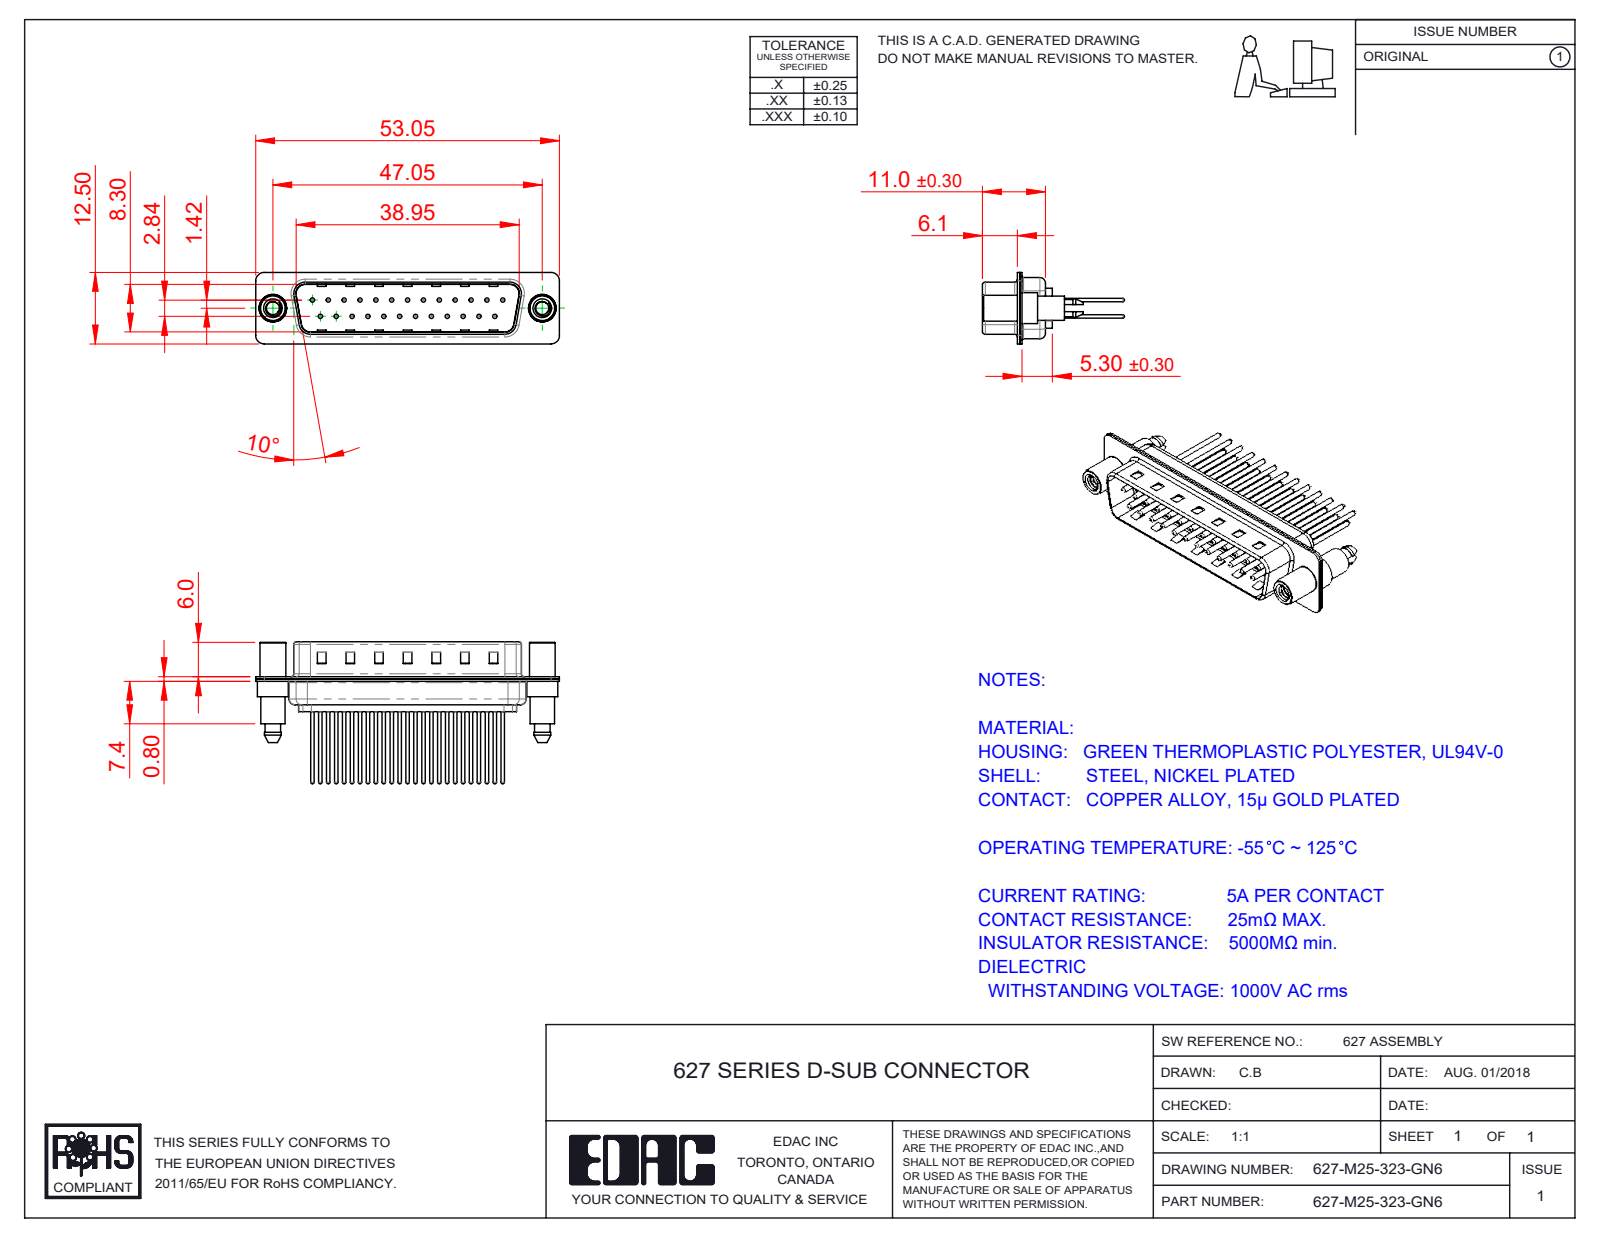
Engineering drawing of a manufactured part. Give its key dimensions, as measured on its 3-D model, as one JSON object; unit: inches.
{"part_name": "627-M25-323-GN6; 627M Housing_25 Contacts; 627M 4-40 Threaded Standoff and Boardlock; 627M Shell Front_25 Contacts (+3 more)", "step_written_by": "SolidWorks 2020 (CONFIG_CONTROL_DESIGN)", "units": "inches", "bodies": {"solids": 30, "faces": 1353, "planar": 364, "cylindrical": 515, "other": 474}, "overall_size": [2.089, 0.975, 0.492], "volume_in3": 0.19, "surface_area_in2": 11.83, "round_holes": [[0.03, 25], [0.063, 25], [0.079, 25], [0.089, 2], [0.157, 2], [0.189, 2]], "round_bosses_or_shafts": [[0.059, 25], [0.024, 25], [0.213, 2], [0.193, 2], [0.177, 2], [0.167, 2]], "partial_cylinders_radius": [[0.059, 18], [0.079, 12], [0.063, 10], [0.02, 8], [0.01, 4], [0.024, 4], [0.026, 4], [0.035, 4]], "face_to_face_distances": [0.016, 0.031, 0.374, 0.358, 0.343, 0.39, 0.047, 0.224, 0.24, 0.03], "hole_center_spacings": [0.124, 0.109, 0.218, 0.327, 0.436, 0.545, 0.654, 0.198]}
